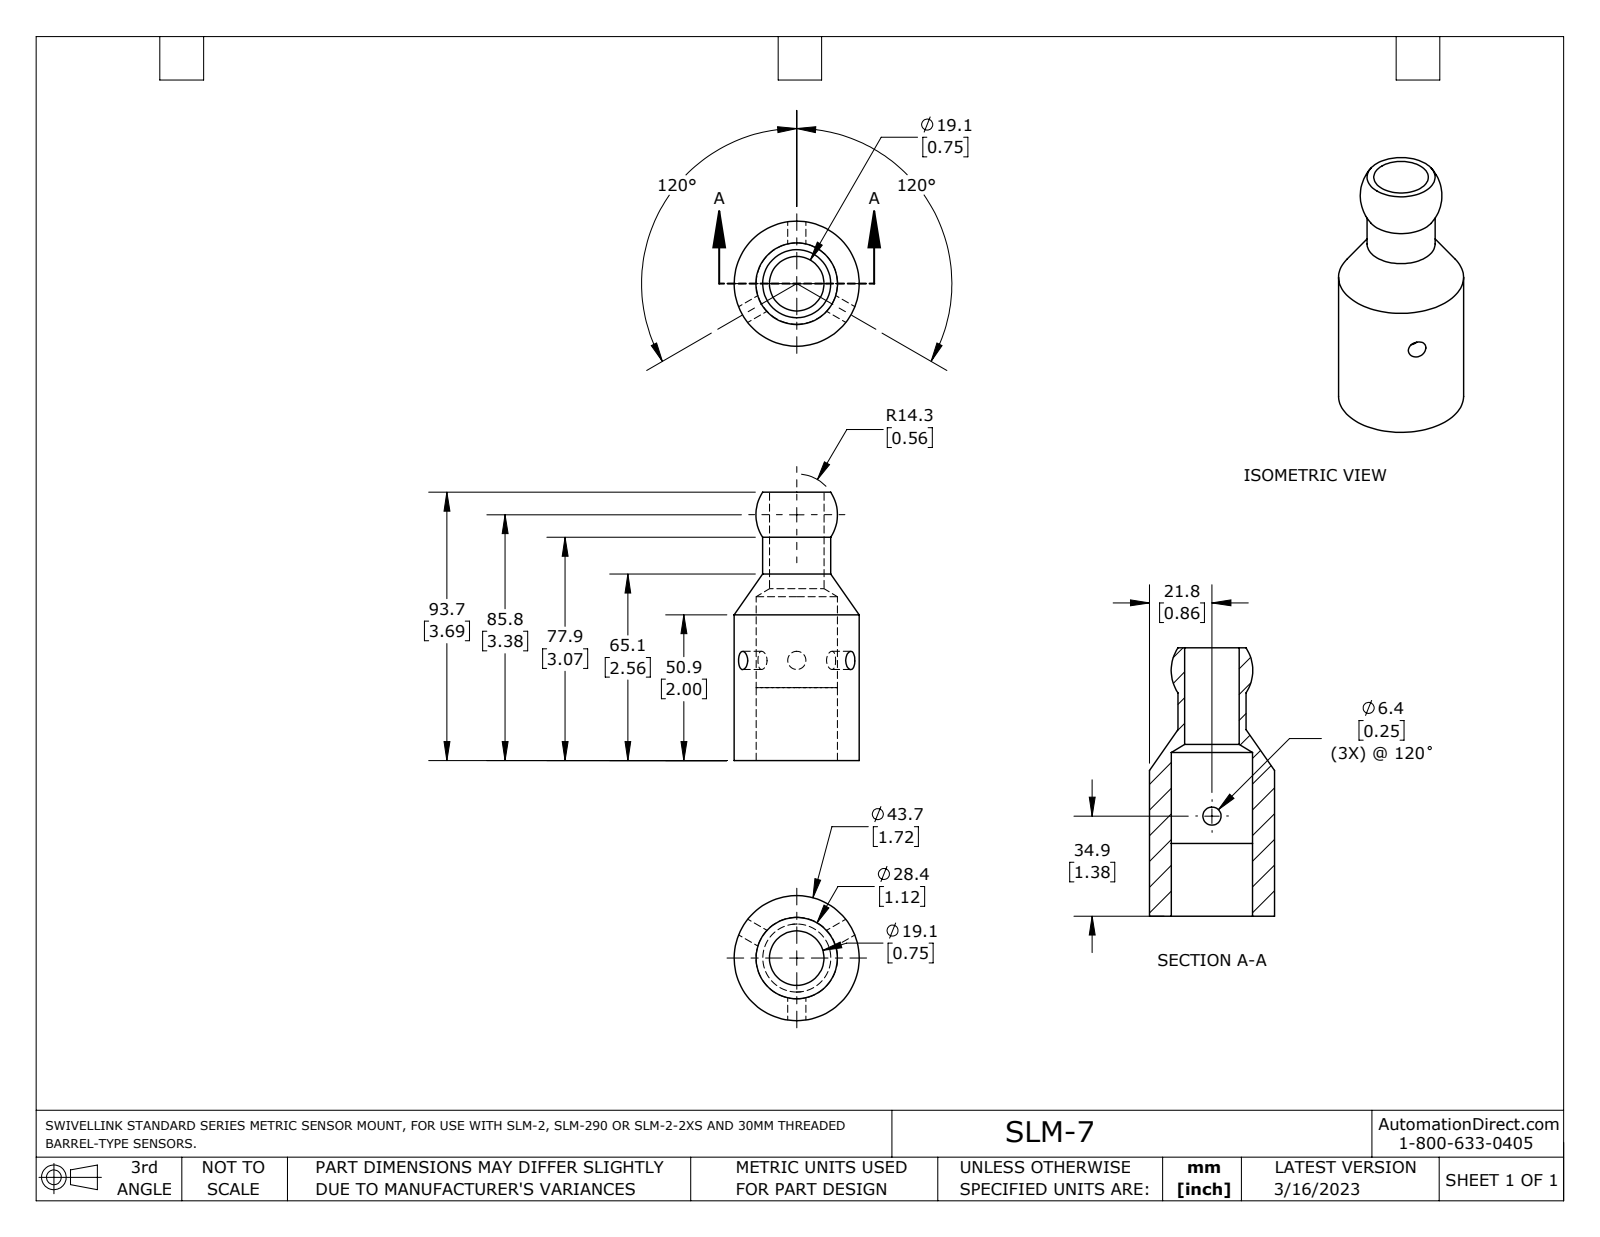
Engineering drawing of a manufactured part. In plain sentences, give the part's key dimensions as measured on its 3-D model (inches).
The part is named "SLM-7". Its 3-D file was written by "SolidWorks 2021 (AUTOMOTIVE_DESIGN)". It is 1 solid with 14 faces: 2 planar, 8 cylindrical and 4 other. Overall it measures 3.939 by 1.719 by 1.719 inches. Its volume is 2.689 cubic inches and its surface area 30.57 square inches. Round holes: 3 of diameter 0.25, 1 of diameter 0.75, 1 of diameter 1.117. Round bosses or shafts: 1 of diameter 1.719, 1 of diameter 0.935. The main face-to-face distances are 3.687.
